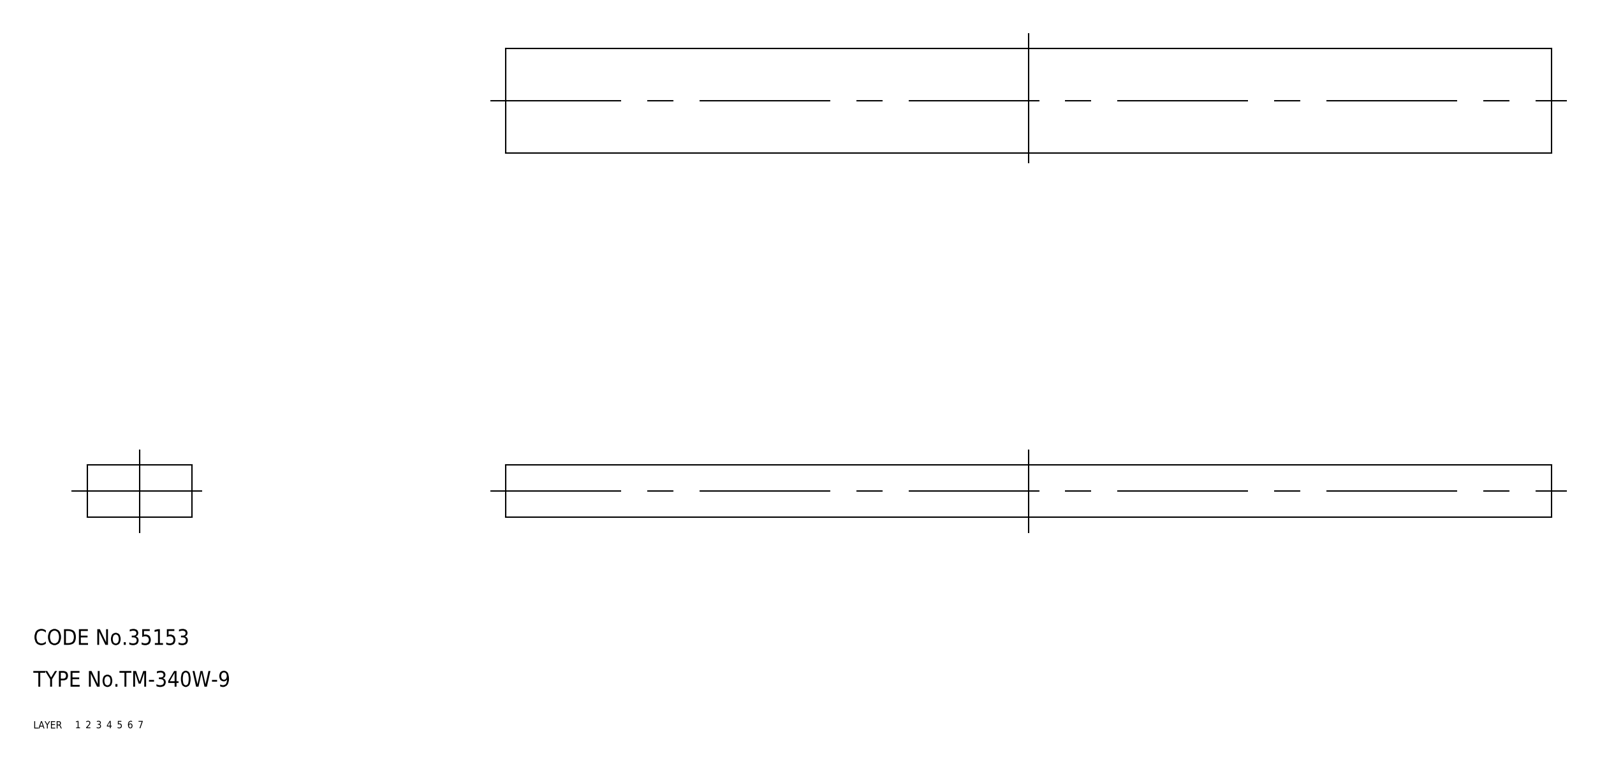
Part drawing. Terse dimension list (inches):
name: TM_340W_9; rubber foam
written by: SolidWorks 2015 (AUTOMOTIVE_DESIGN)
unit: in
bodies: 1 solid, 6 faces (6 planar, 0 cylindrical, 0 other)
size: 7.874 × 0.787 × 0.394
volume: 2.441 in³; area: 19.22 in²
face distances: 0.394, 0.787, 7.874
